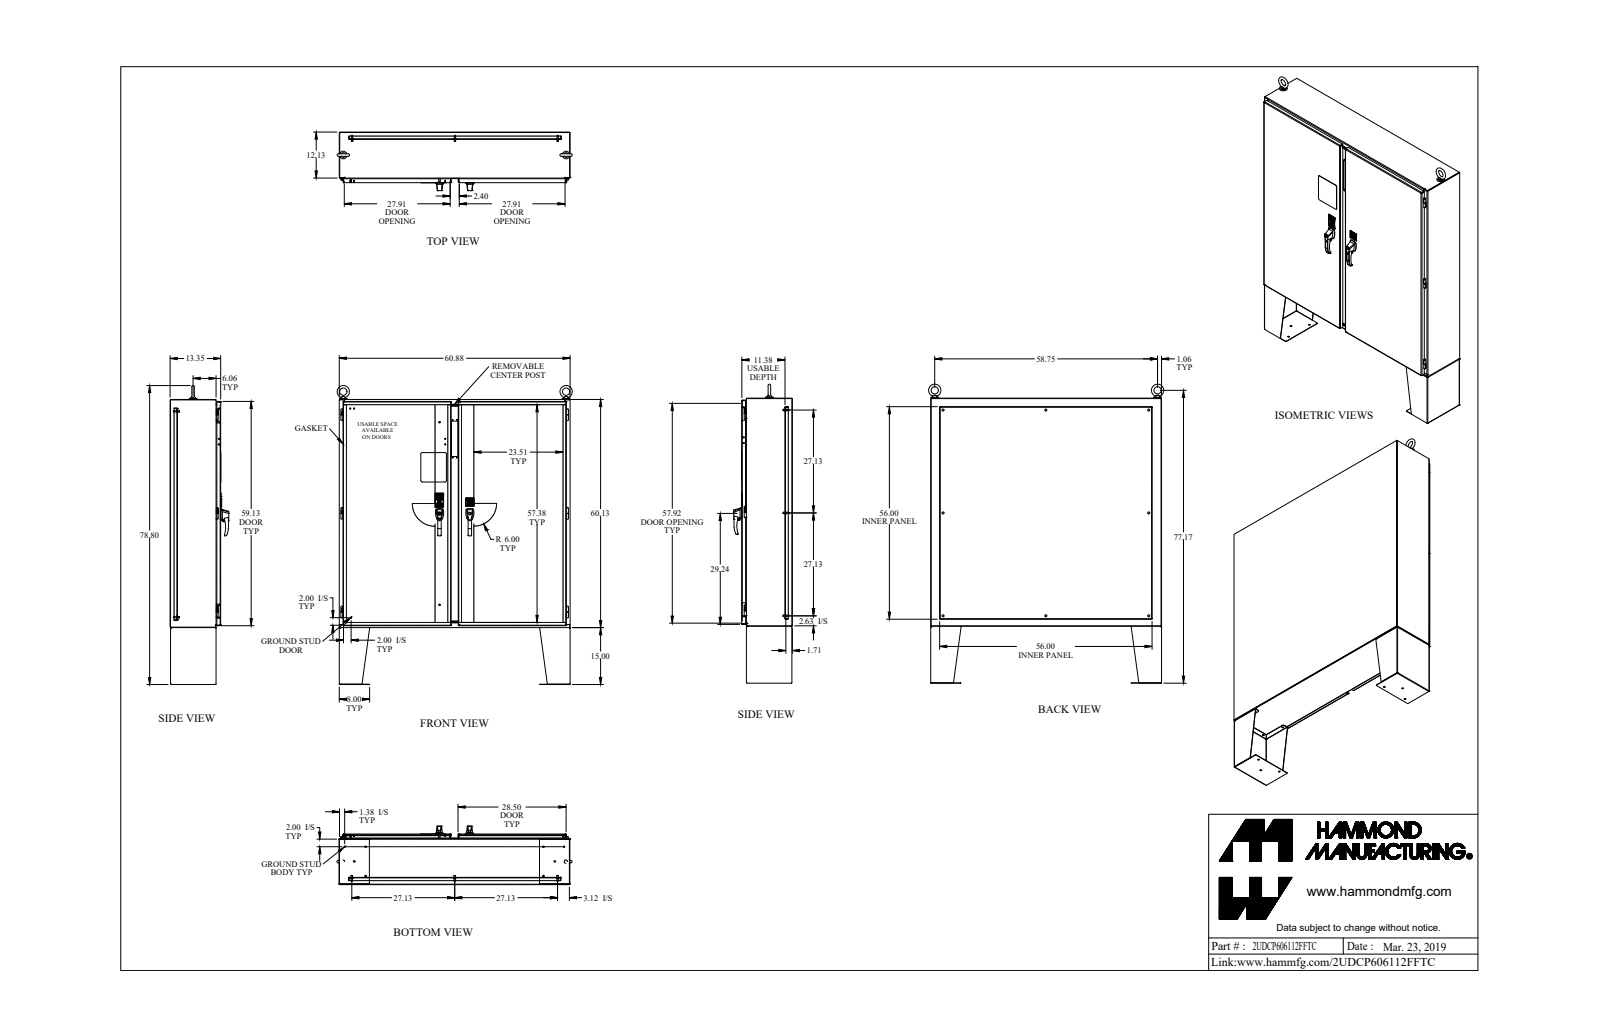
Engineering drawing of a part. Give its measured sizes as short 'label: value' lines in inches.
name: 2UDCP606112FFTC
written by: SolidWorks 2018 (AUTOMOTIVE_DESIGN)
unit: in
bodies: 178 solids, 2694 faces (1564 planar, 810 cylindrical, 320 other)
size: 78.799 × 61.997 × 15.465
volume: 3 355 in³; area: 35 155 in²
holes: 14× ⌀0.437, 10× ⌀0.307, 9× ⌀0.281, 8× ⌀0.25, 8× ⌀0.35, 6× ⌀0.313, 5× ⌀0.196, 5× ⌀0.445, 4× ⌀0.257, 4× ⌀0.28, 4× ⌀0.39, 4× ⌀0.413
bosses: 14× ⌀0.25, 12× ⌀1, 9× ⌀0.375, 8× ⌀0.65, 8× ⌀0.33, 8× ⌀0.281, 5× ⌀0.625, 4× ⌀0.75
rounds: 54× R0.06, 44× R0.125, 38× R0.5, 32× R0.017, 29× R0.185, 16× R0.048, 16× R0.143, 13× R0.318
face distances: 0.125, 0.072, 11.431, 13.368, 13.243, 1.937, 1.812, 1.865, 1.741, 11.503
hole spacings: 7.996, 1.287, 4.888, 6.228, 7.456, 8.074, 9.964, 10.99
